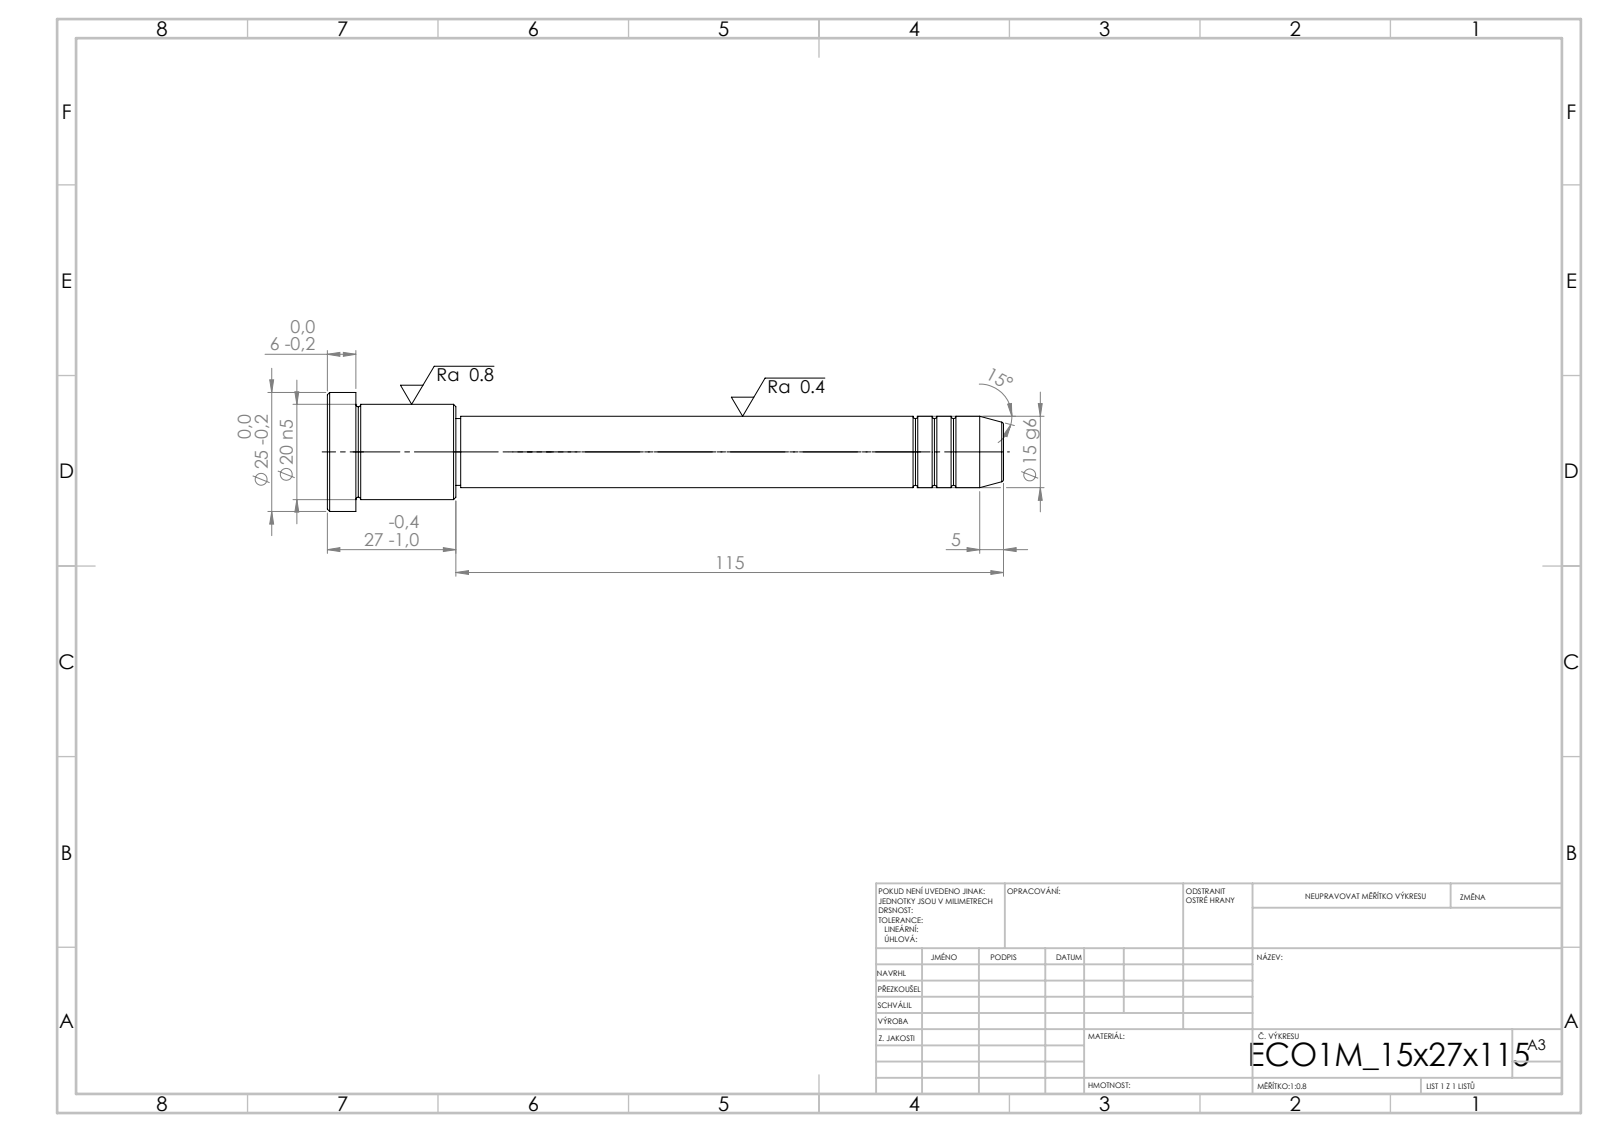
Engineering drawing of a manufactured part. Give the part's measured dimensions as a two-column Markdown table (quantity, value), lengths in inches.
| quantity | value |
| --- | --- |
| STEP written by | SolidWorks 2019 (CONFIG_CONTROL_DESIGN) |
| units | inches |
| bodies | 1 solid, 43 faces (5 planar, 14 cylindrical, 24 other) |
| overall size | 5.591 × 0.984 × 0.984 |
| volume | 1.806 in³ |
| surface area | 12.74 in² |
| round bosses / shafts (diameter × count) | 0.984 × 1, 0.787 × 1, 0.591 × 1, 0.551 × 1 |
| main face-to-face distances | 0.236, 0.827, 1.063, 4.528, 5.354, 5.591, 4.488, 0.039, 0.866, 1.102 |
